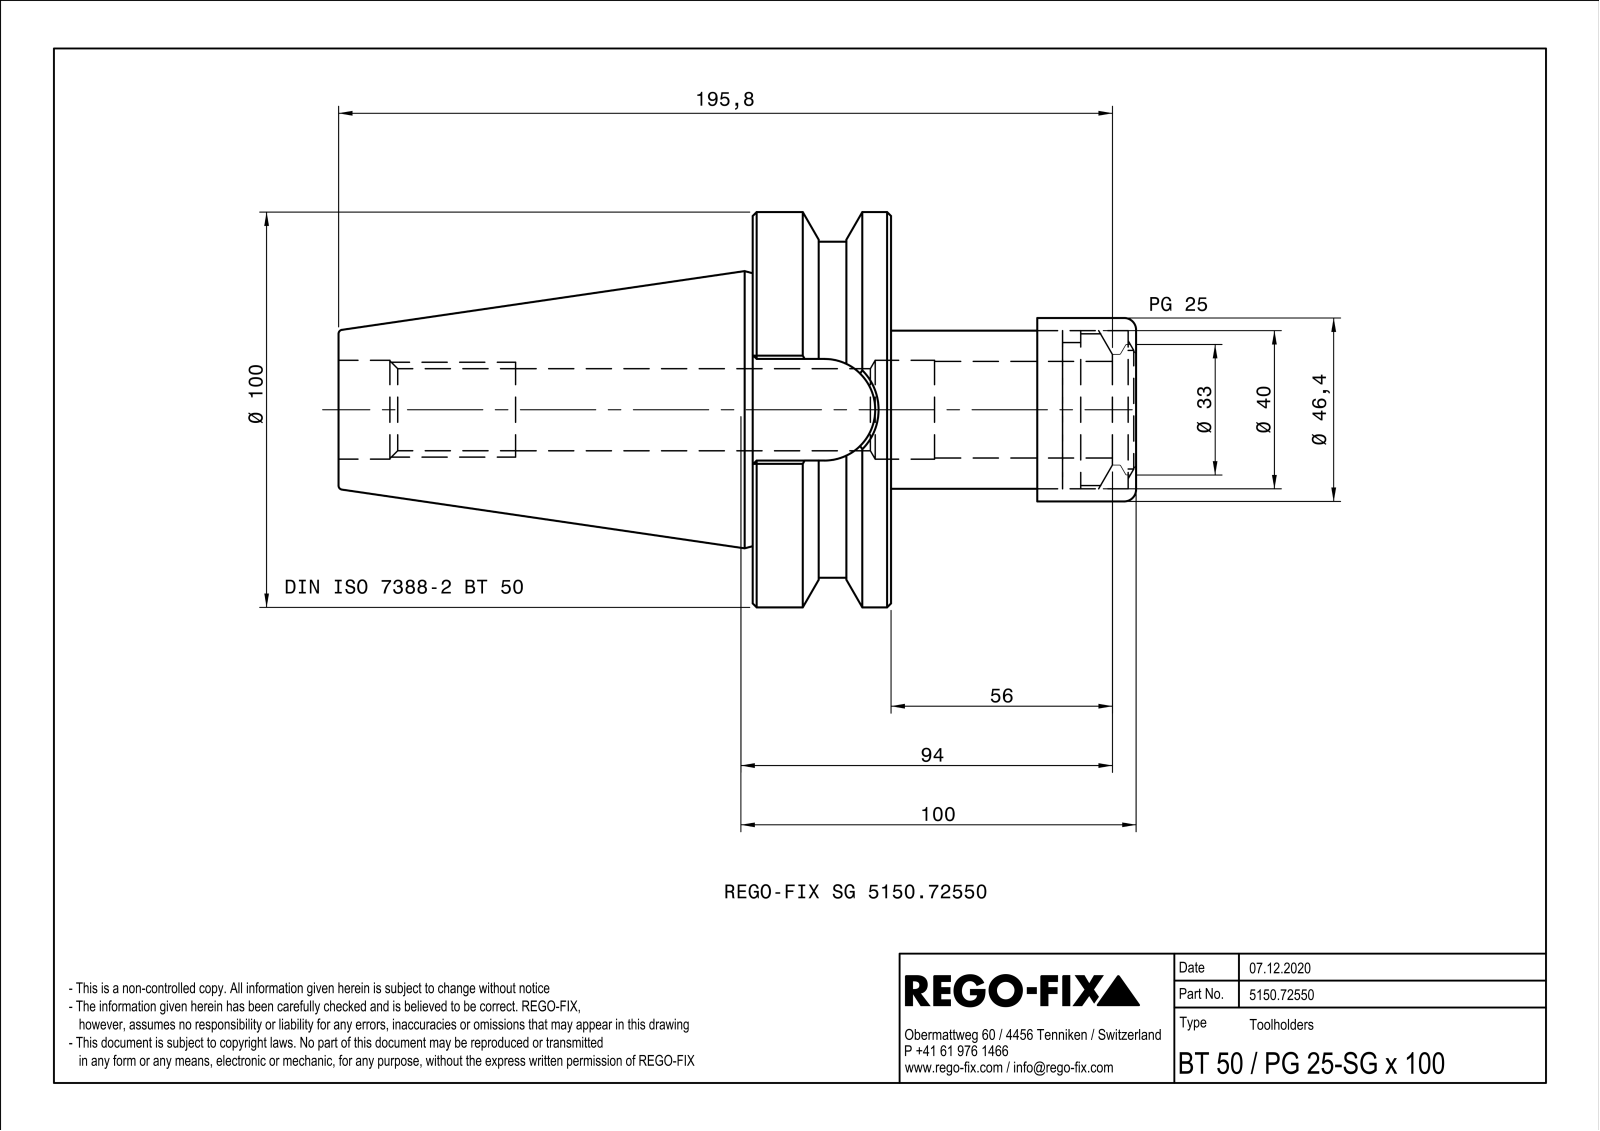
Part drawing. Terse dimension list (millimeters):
name: 0015537
written by: SIEMENS PLM Software Solid Edge ST10 (AUTOMOTIVE_DESIGN)
unit: mm
bodies: 2 solids, 97 faces (34 planar, 24 cylindrical, 39 other)
size: 201.8 × 100 × 100
volume: 494 877 mm³; area: 73 057 mm²
holes: 1× ⌀20.75, 1× ⌀25, 1× ⌀30, 1× ⌀38.38, 1× ⌀40.05, 1× ⌀42
bosses: 1× ⌀100, 1× ⌀85, 1× ⌀46.4, 1× ⌀46, 1× ⌀40, 1× ⌀34
rounds: 4× R0.5, 1× R12.85
face distances: 35, 70.7, 139.8, 104.8, 62, 97, 201.8, 37, 25, 72
